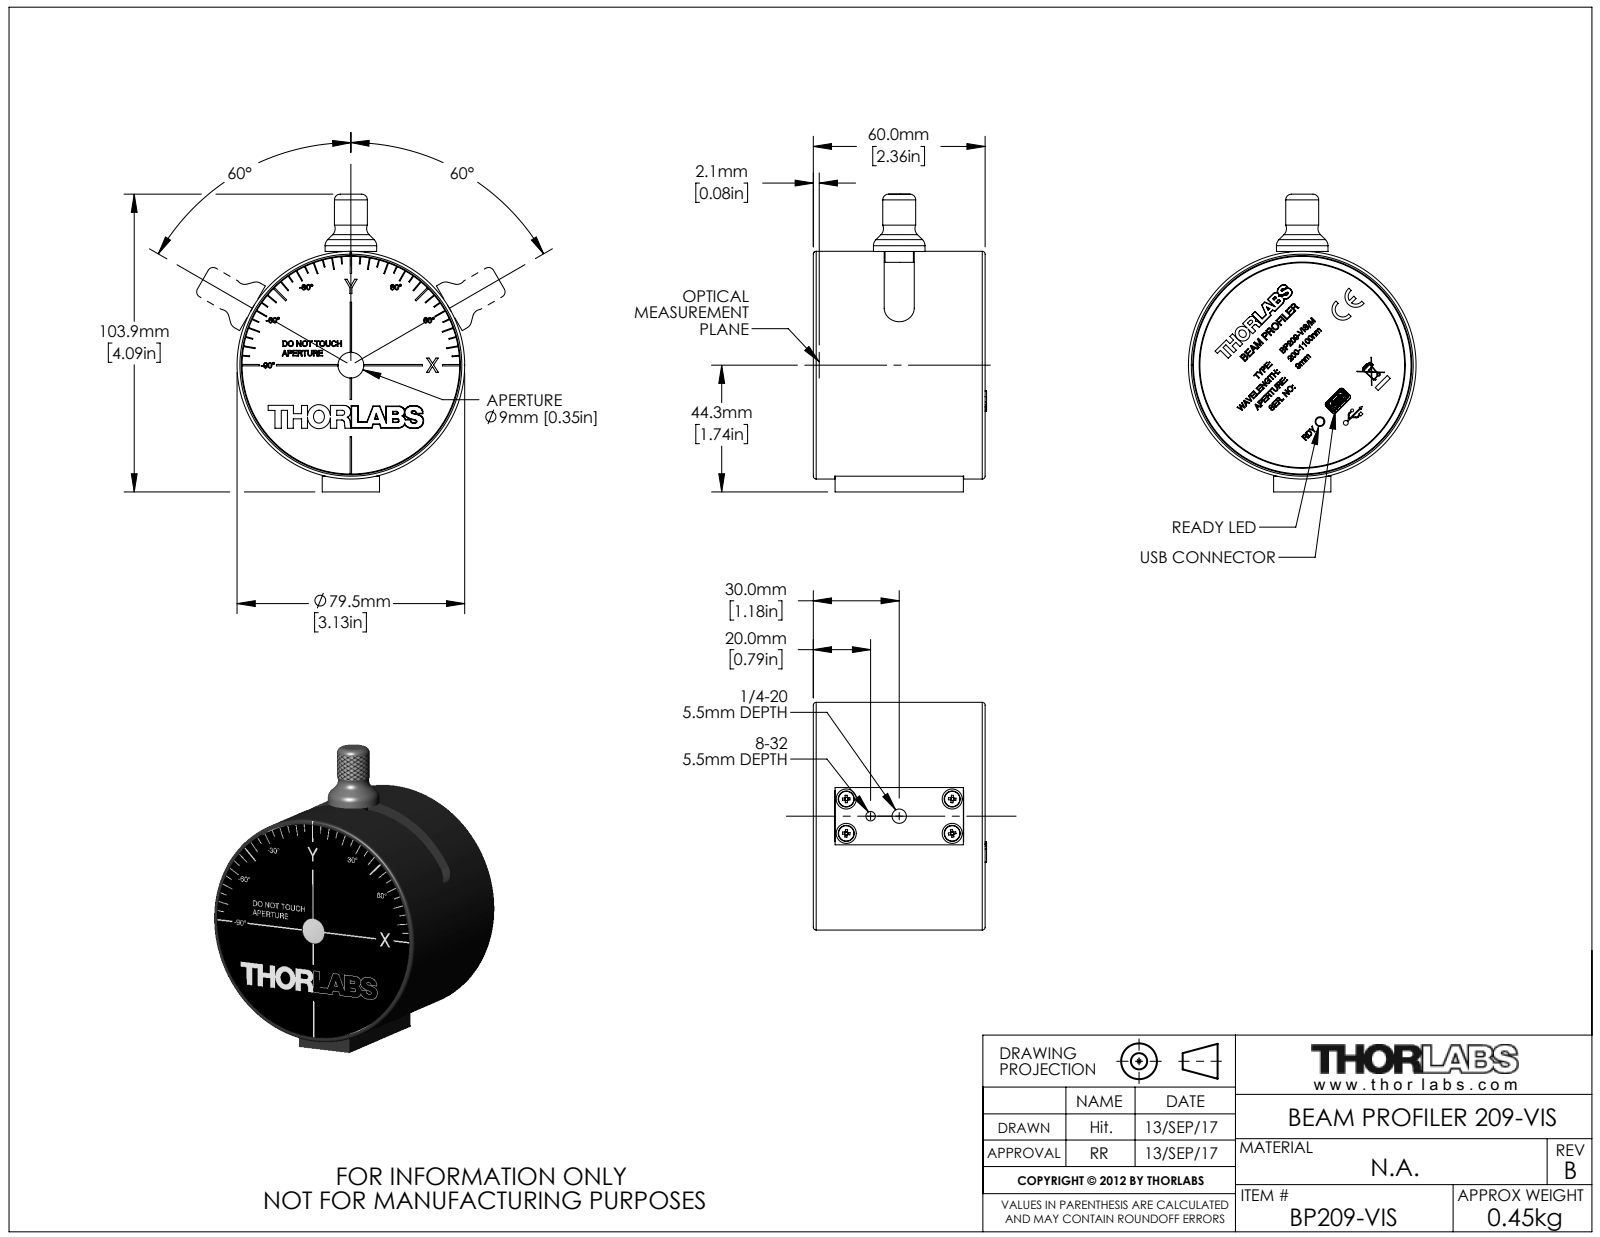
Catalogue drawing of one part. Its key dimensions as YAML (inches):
part_name: "21424-E0W"
step_written_by: "SolidWorks 2012 (CONFIG_CONTROL_DESIGN)"
units: inches
bodies: {solids: 14, faces: 3705, planar: 2598, cylindrical: 408, other: 699}
overall_size: [4.093, 3.13, 2.382]
volume: 6.005
surface_area: 153.8
round_holes:
  - {diameter: 0.126, count: 10}
  - {diameter: 0.087, count: 9}
  - {diameter: 0.315, count: 8}
  - {diameter: 0.063, count: 6}
  - {diameter: 0.248, count: 6}
  - {diameter: 0.197, count: 5}
  - {diameter: 0.276, count: 5}
  - {diameter: 0.098, count: 4}
  - {diameter: 0.209, count: 4}
  - {diameter: 0.039, count: 1}
  - {diameter: 0.051, count: 1}
  - {diameter: 0.066, count: 1}
round_bosses_or_shafts:
  - {diameter: 0.22, count: 4}
  - {diameter: 0.118, count: 4}
  - {diameter: 0.031, count: 2}
  - {diameter: 3.13, count: 1}
  - {diameter: 2.992, count: 1}
  - {diameter: 2.839, count: 1}
  - {diameter: 2.827, count: 1}
  - {diameter: 2.815, count: 1}
partial_cylinders:
  - {radius: 0.059, count: 18}
  - {radius: 0.157, count: 16}
  - {radius: 0.004, count: 14}
  - {radius: 0.008, count: 14}
  - {radius: 0.039, count: 14}
  - {radius: 0.012, count: 9}
  - {radius: 0.028, count: 8}
  - {radius: 0.197, count: 8}
face_to_face_distances: [0.039, 2.323, 2.35, 2.362, 2.283, 0.028, 2.311, 0.02, 0.079, 0.059]
hole_center_spacings: [0.934, 1.22, 1.726, 2.255, 1.063, 1.841, 1.063, 0.766]
